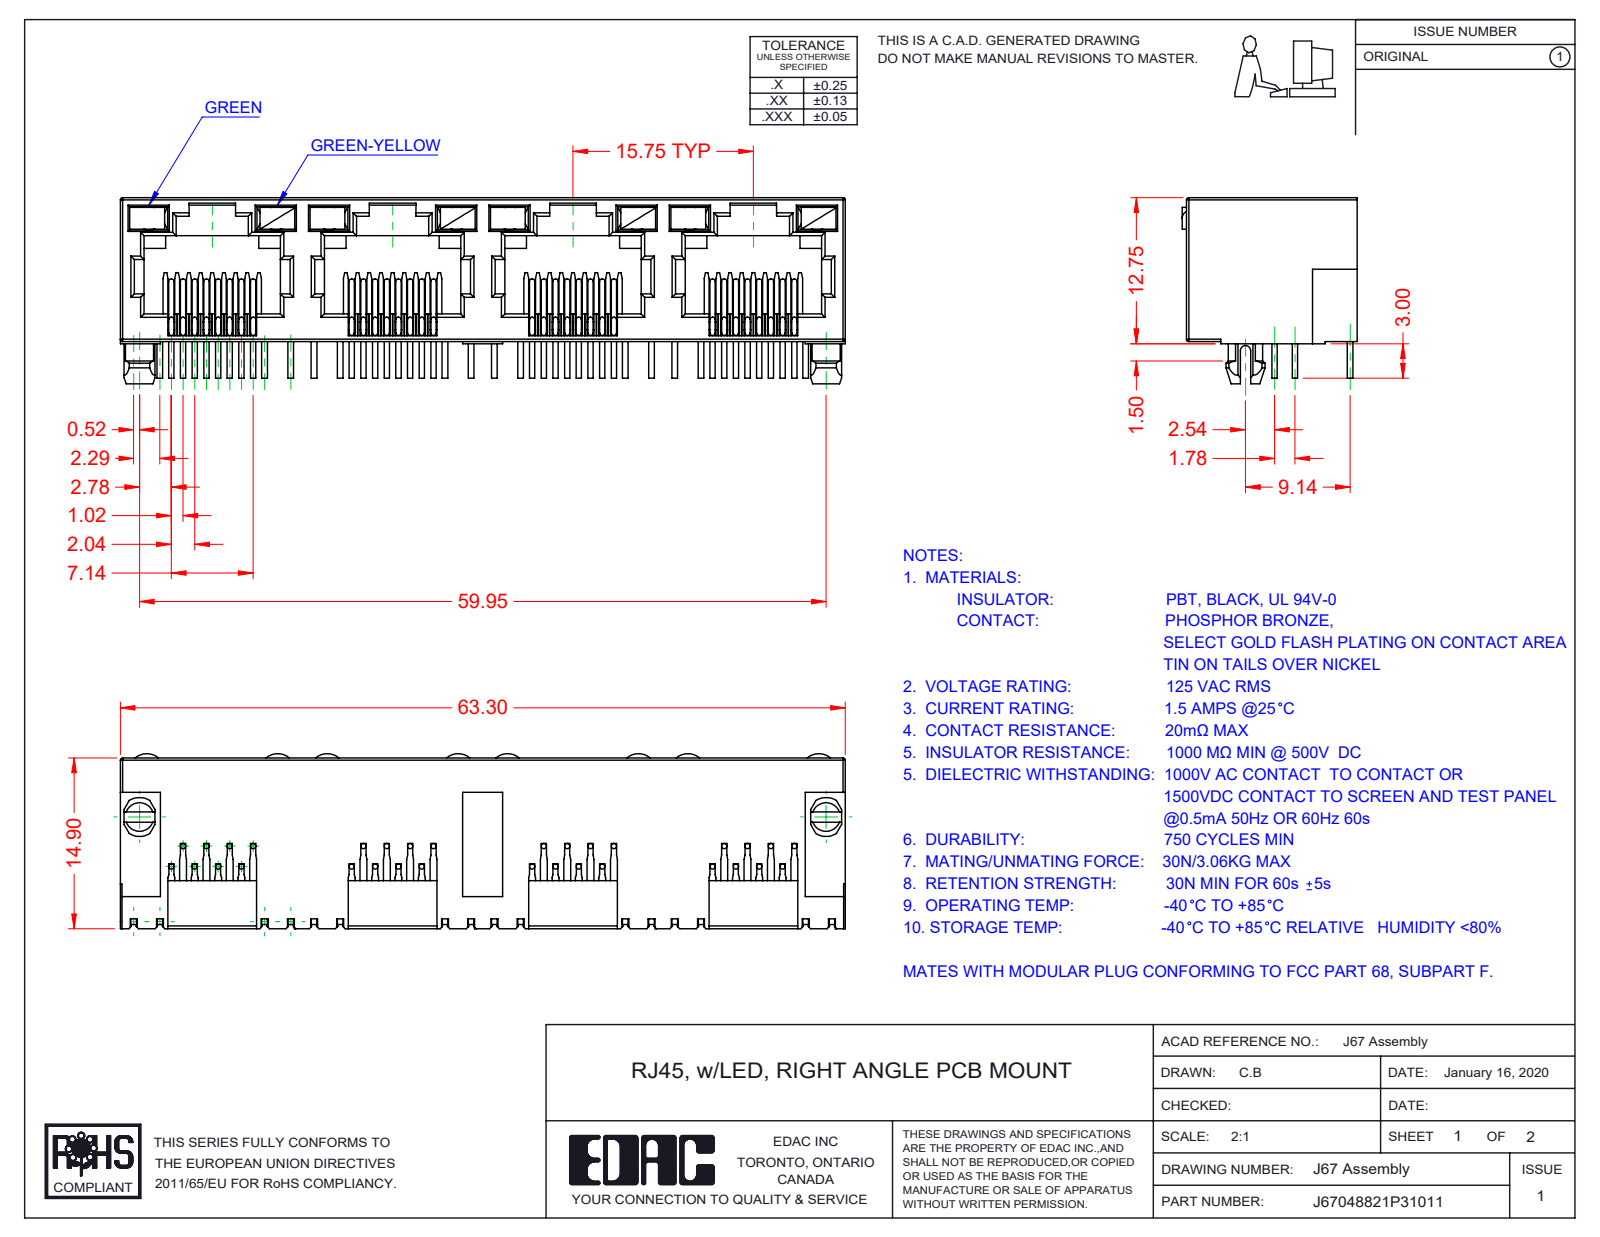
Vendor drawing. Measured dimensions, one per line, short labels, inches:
name: J67048822P35011; 67 Contacts; 67 LED RH_5-Green-Yellow; 67 LED LH_3-Green (+1 more)
written by: SolidWorks 2016 (CONFIG_CONTROL_DESIGN)
unit: in
bodies: 41 solids, 2473 faces (1781 planar, 484 cylindrical, 208 other)
size: 2.492 × 0.64 × 0.602
volume: 0.315 in³; area: 17.94 in²
bosses: 96× ⌀0.018
rounds: 66× R0.008, 29× R0.012, 9× R0.018, 8× R0.061, 2× R0.059, 2× R0.067, 1× R0.014, 1× R0.039
face distances: 0.02, 0.494, 0.074, 0.035, 0.394, 0.62, 0.039, 0.055, 0.433, 0.468
